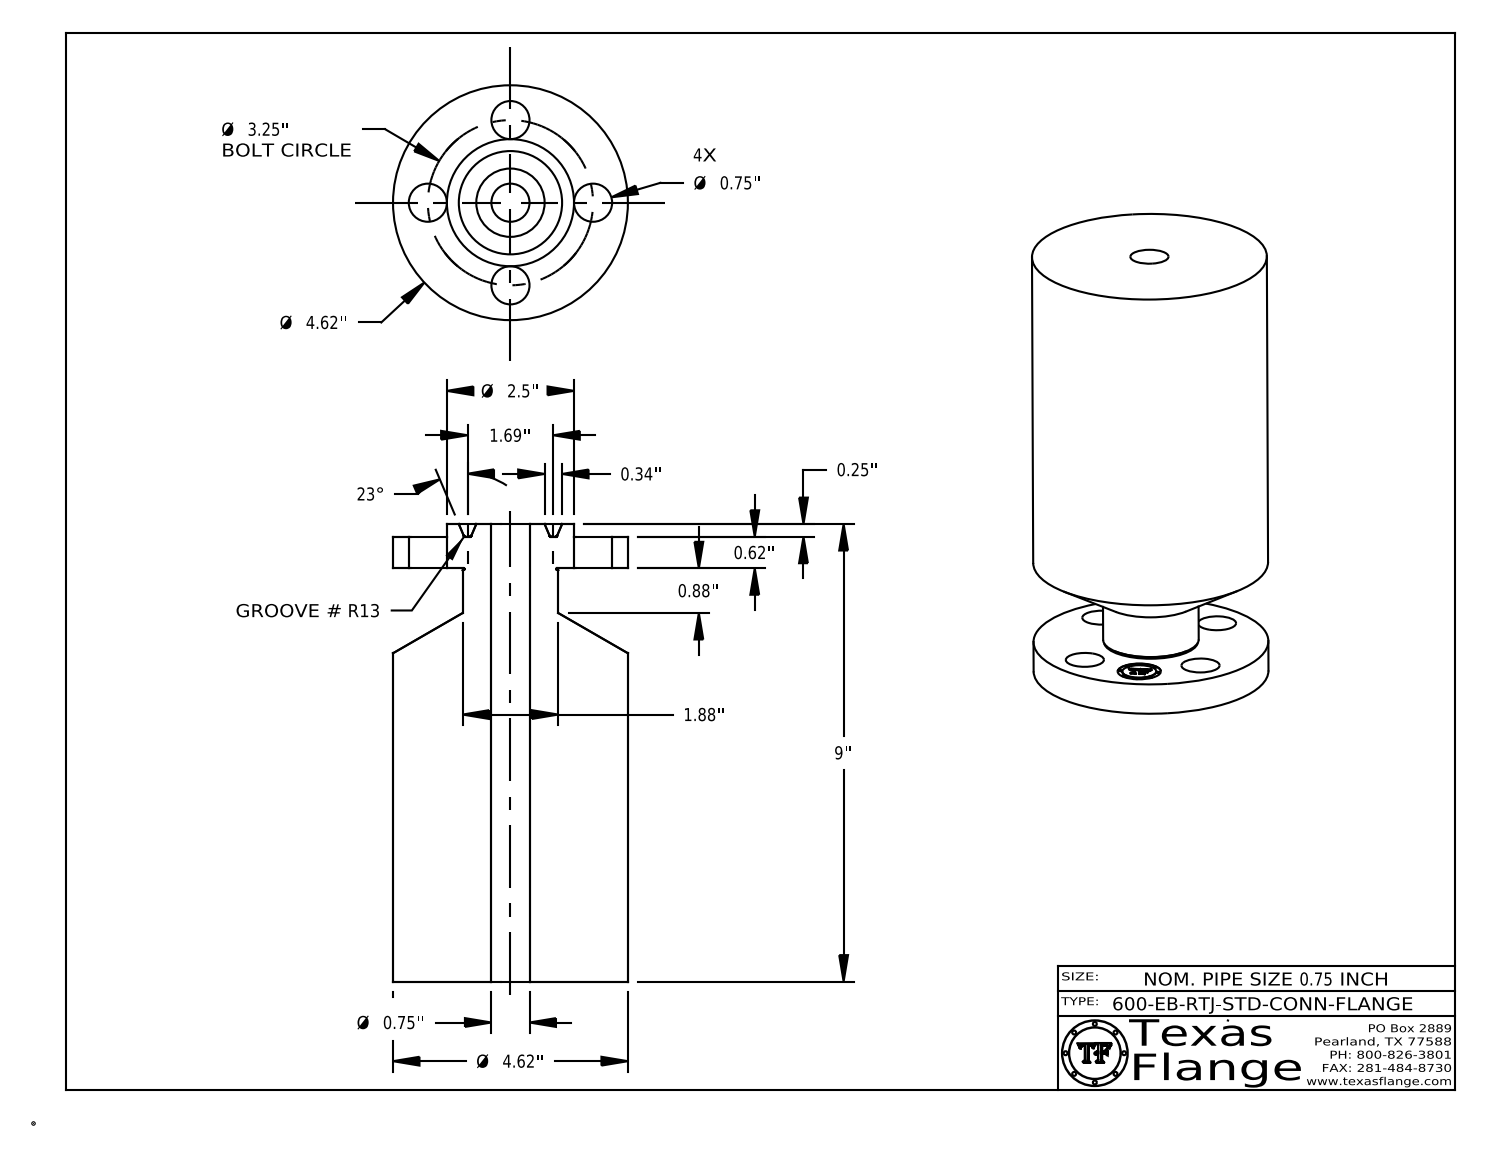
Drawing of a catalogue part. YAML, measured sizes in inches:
part_name: "0.75-600-EB-RTJ-STD-CONN-FLANGE"
step_written_by: "CATIA V5 STEP AP214 (AUTOMOTIVE_DESIGN)"
units: inches
bodies: {solids: 1, faces: 423, planar: 371, cylindrical: 38, other: 14}
overall_size: [9, 4.62, 4.62]
volume: 123.9
surface_area: 198.2
round_holes:
  - {diameter: 0.75, count: 5}
  - {diameter: 0.85, count: 1}
round_bosses_or_shafts:
  - {diameter: 0.051, count: 8}
  - {diameter: 4.62, count: 1}
  - {diameter: 2.5, count: 1}
  - {diameter: 1.88, count: 1}
  - {diameter: 0.67, count: 1}
face_to_face_distances: [8.13, 0.62, 8.75, 0.25, 0.87, 9, 0.865, 0.615, 8.135, 0.254]
hole_center_spacings: [1.625, 2.298, 1.244, 3.003, 3.25]
